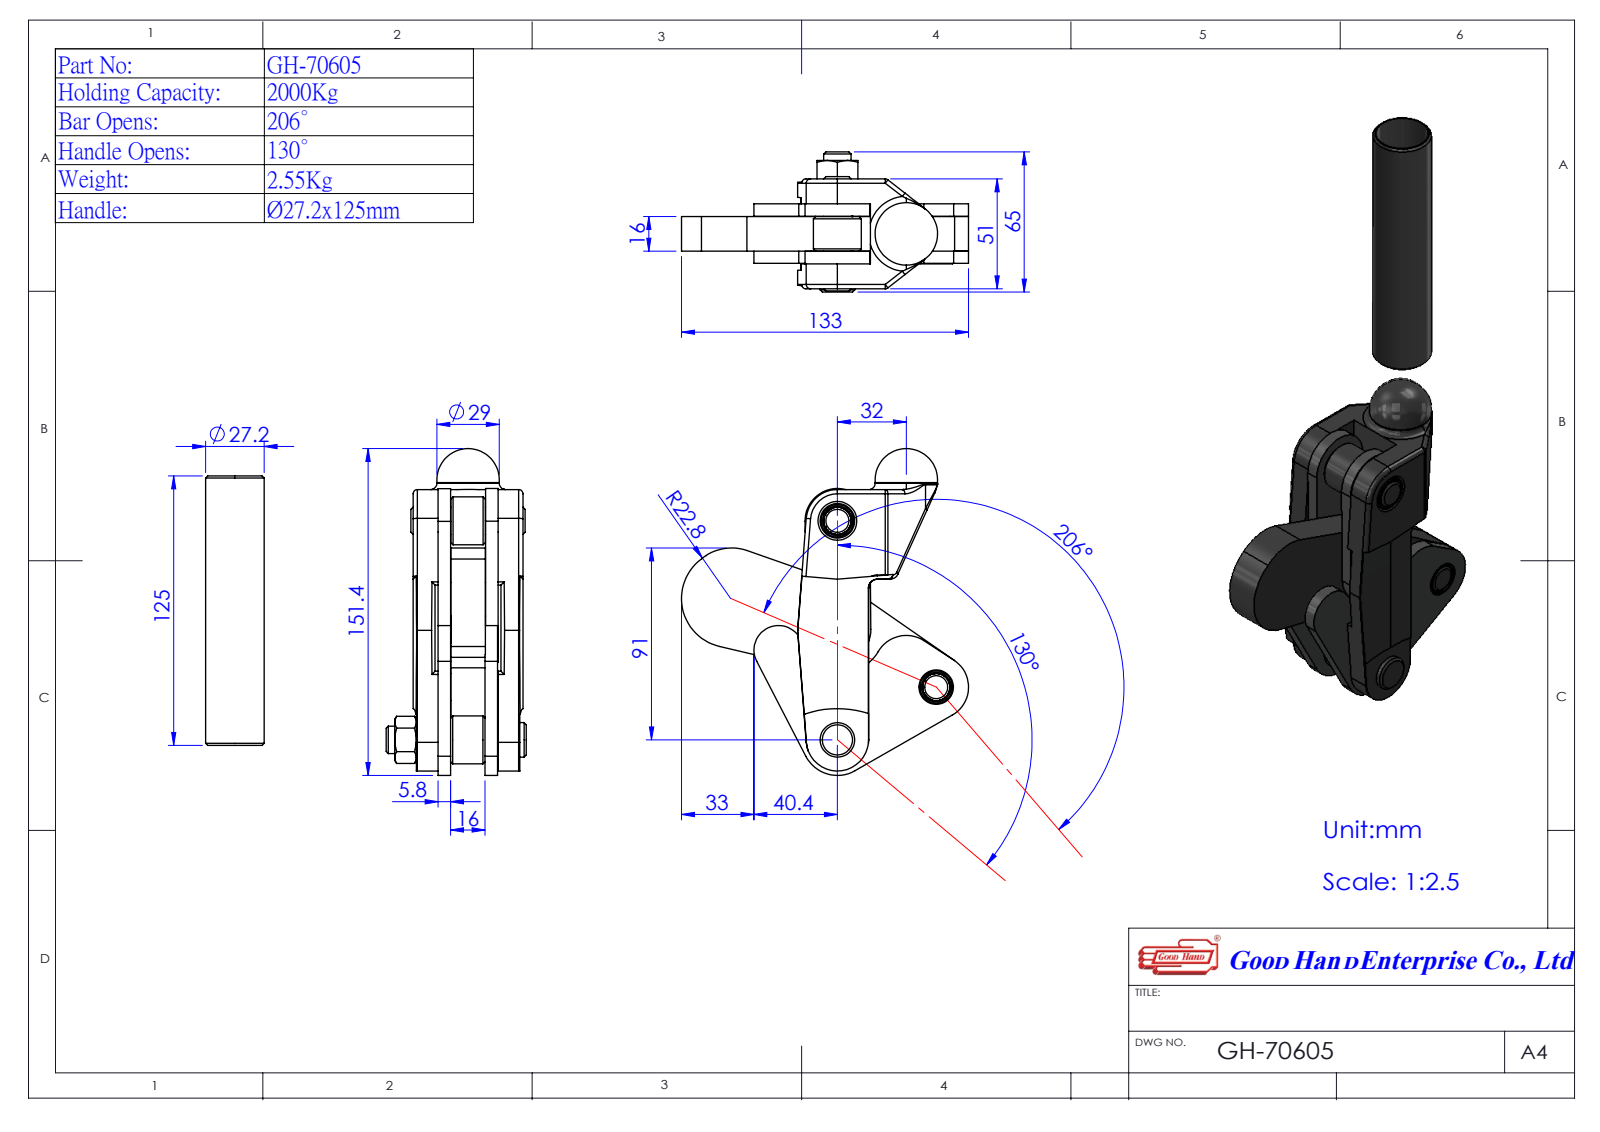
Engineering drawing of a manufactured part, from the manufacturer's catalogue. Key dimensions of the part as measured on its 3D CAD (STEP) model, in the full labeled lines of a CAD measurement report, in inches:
Part name (STEP PRODUCT): Group1^GH-70605(簡化); 3700908-1^GH-70605(簡化); GH-70605(簡化); Group5^GH-70605(簡化) (+2 more)
STEP written by: SolidWorks 2016 (AUTOMOTIVE_DESIGN)
Units: inches
Bodies: 5 solids, 147 faces (61 planar, 68 cylindrical, 18 other)
Overall size (bounding box): 10.884 × 5.244 × 2.559
Volume: 20.22 in³ · Surface area: 156.8 in²
Round holes (diameter × count): ⌀0.5 ×3, ⌀0.874 ×1
Round bosses / shafts (diameter × count): ⌀0.63 ×2, ⌀0.498 ×2, ⌀1.071 ×1, ⌀0.874 ×1, ⌀0.5 ×1
Partial cylindrical surfaces — rounded edges, fillets, slot ends (radius × count): R0.571 ×4, R0.591 ×4, R0.157 ×2, R0.448 ×1, R0.65 ×1, R0.725 ×1, R0.866 ×1, R0.898 ×1
Main face-to-face distances: 0.228, 0.868, 1.096, 0.689, 1.319, 0.64, 0.863, 0.635, 0.233, 0.233
Hole centre spacings: 1.984, 2.012, 2.046
